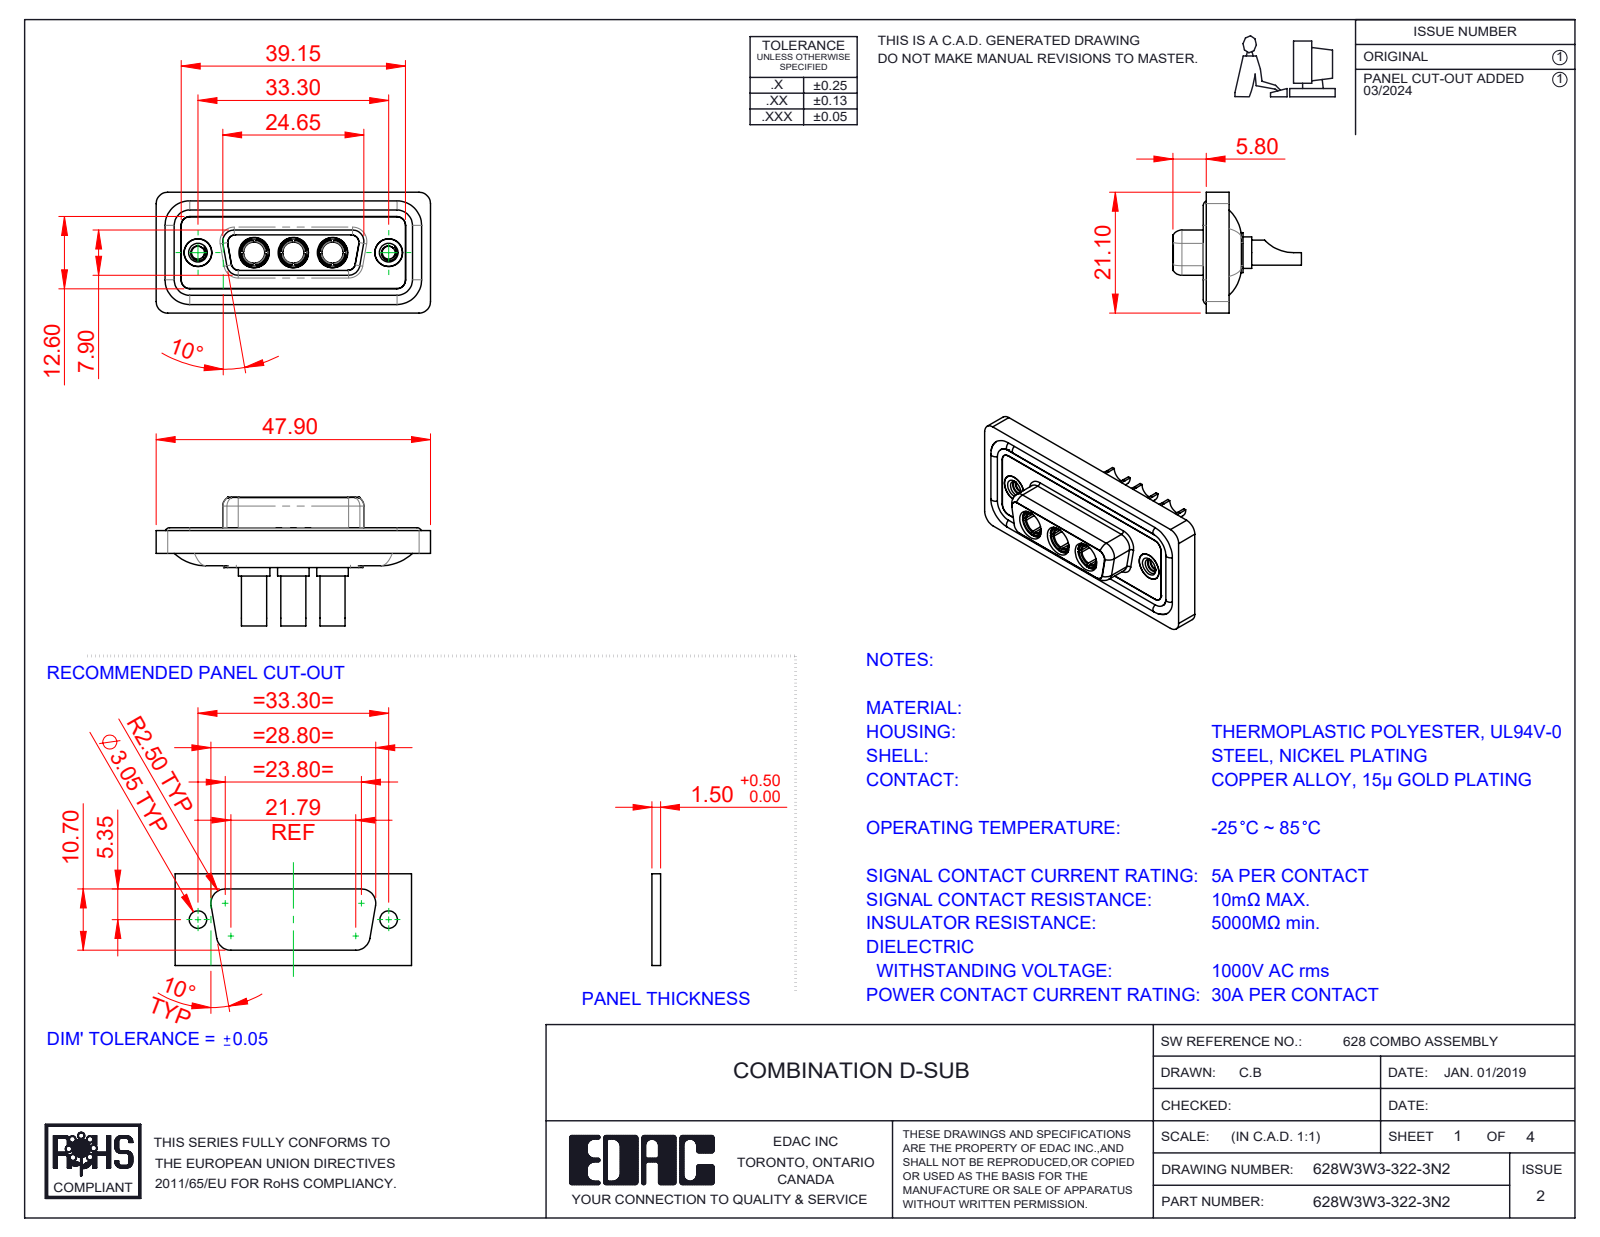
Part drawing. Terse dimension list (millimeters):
name: 628Combo Threaded Rivet_2; 628Combo Housing_3W3; Power Socket_30A SC; 628W3W3-322-3N2 (+3 more)
written by: SolidWorks 2023 (CONFIG_CONTROL_DESIGN)
unit: mm
bodies: 13 solids, 626 faces (201 planar, 266 cylindrical, 159 other)
size: 47.9 × 22.45 × 21.1
volume: 6 098 mm³; area: 10 061 mm²
holes: 5× ⌀4.85, 3× ⌀3.5, 3× ⌀3.7, 3× ⌀5.3, 2× ⌀2.26, 2× ⌀4, 2× ⌀4.05, 2× ⌀5
bosses: 4× ⌀1.6, 3× ⌀5.5, 3× ⌀5.2, 3× ⌀4.96, 3× ⌀4.75, 3× ⌀4.4, 3× ⌀3.75, 2× ⌀4.95
rounds: 22× R1.5, 20× R2, 12× R1.35, 8× R1.6, 4× R0.25, 4× R0.5, 4× R0.6, 4× R0.65
face distances: 0.4, 1.8, 1.6, 0.5, 7.45, 1.1, 2.9, 5.65, 7.05, 6.6
hole spacings: 6.85, 9.8, 16.65, 23.5, 13.7, 33.3
